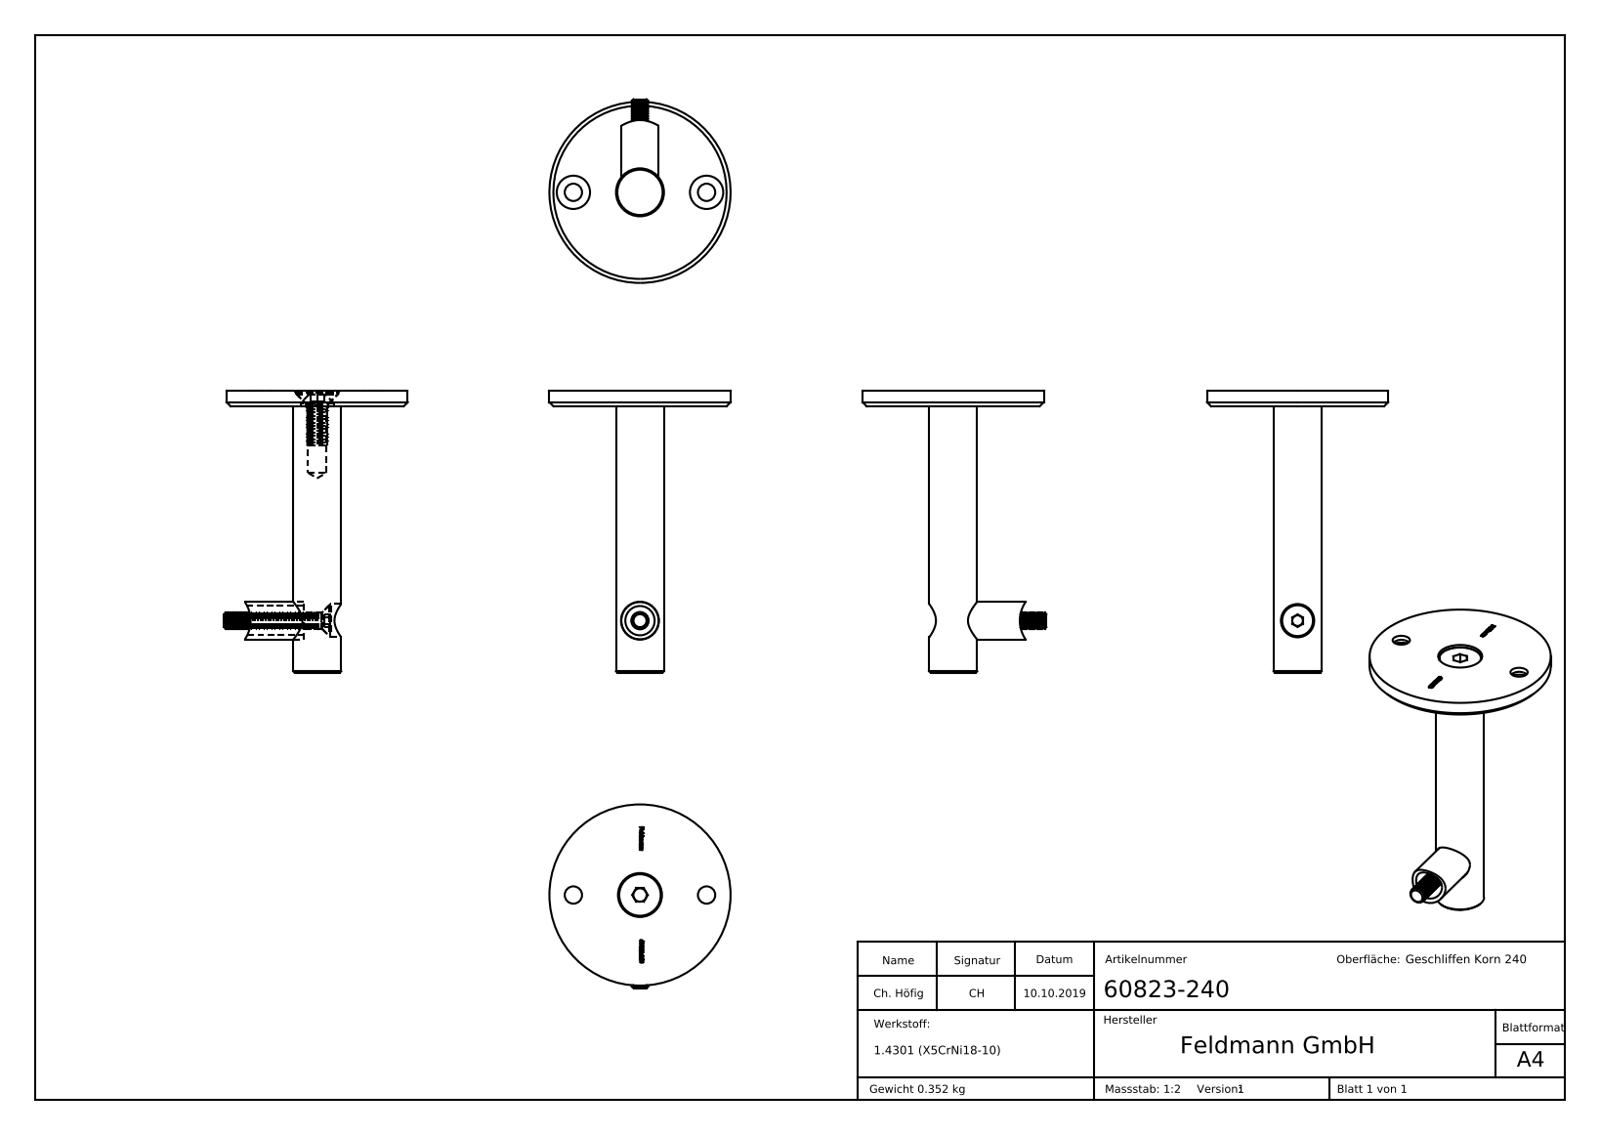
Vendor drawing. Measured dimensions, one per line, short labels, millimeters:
name: socket countersunk head screw_din; 60823-240 Teil3; socket countersunk head screw_din_DIN 7991 - M6 x 40 --- 40S; 60823-240 Teil3_60823-240 Teil3 (+6 more)
written by: SolidWorks 2015 (CONFIG_CONTROL_DESIGN)
unit: mm
bodies: 5 solids, 438 faces (152 planar, 66 cylindrical, 220 other)
size: 106 × 68.95 × 68
volume: 46 497 mm³; area: 19 605 mm²
holes: 3× ⌀6.5, 3× ⌀12.5, 1× ⌀6.8, 1× ⌀8.5, 1× ⌀11, 1× ⌀14.2, 1× ⌀16.5
bosses: 1× ⌀68, 1× ⌀18, 1× ⌀15.57, 1× ⌀14, 1× ⌀11.57, 1× ⌀8, 1× ⌀6
rounds: 1× R12.5
face distances: 6, 100, 106, 105.15, 5.15, 0.85, 10.05, 85.15, 14.85, 20
hole spacings: 25, 50
